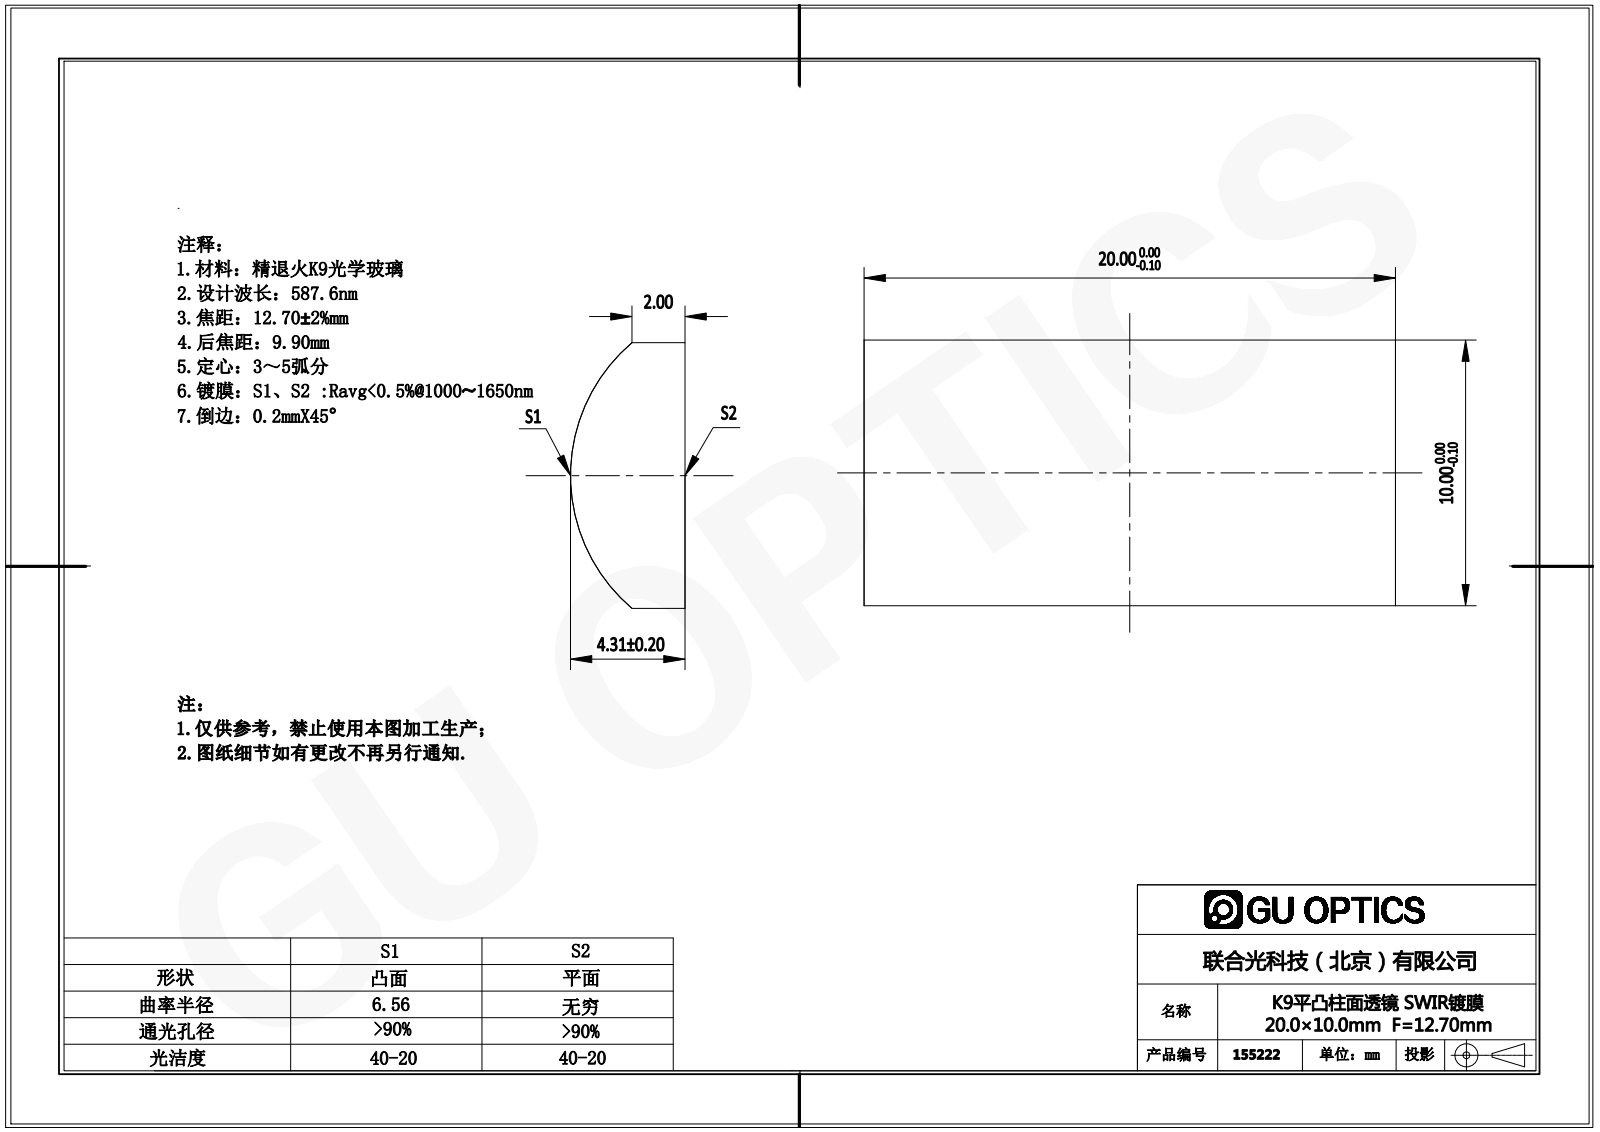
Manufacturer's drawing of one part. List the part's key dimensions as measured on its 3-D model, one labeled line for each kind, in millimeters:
Part name (STEP PRODUCT): 155024
STEP written by: SolidWorks 2016 (AUTOMOTIVE_DESIGN)
Units: millimetres
Bodies: 1 solid, 6 faces (5 planar, 1 cylindrical, 0 other)
Overall size (bounding box): 20 × 10 × 4.31
Volume: 721 mm³ · Surface area: 579 mm²
Partial cylindrical surfaces — rounded edges, fillets, slot ends (radius × count): R6.56 ×1
Main face-to-face distances: 10, 20
